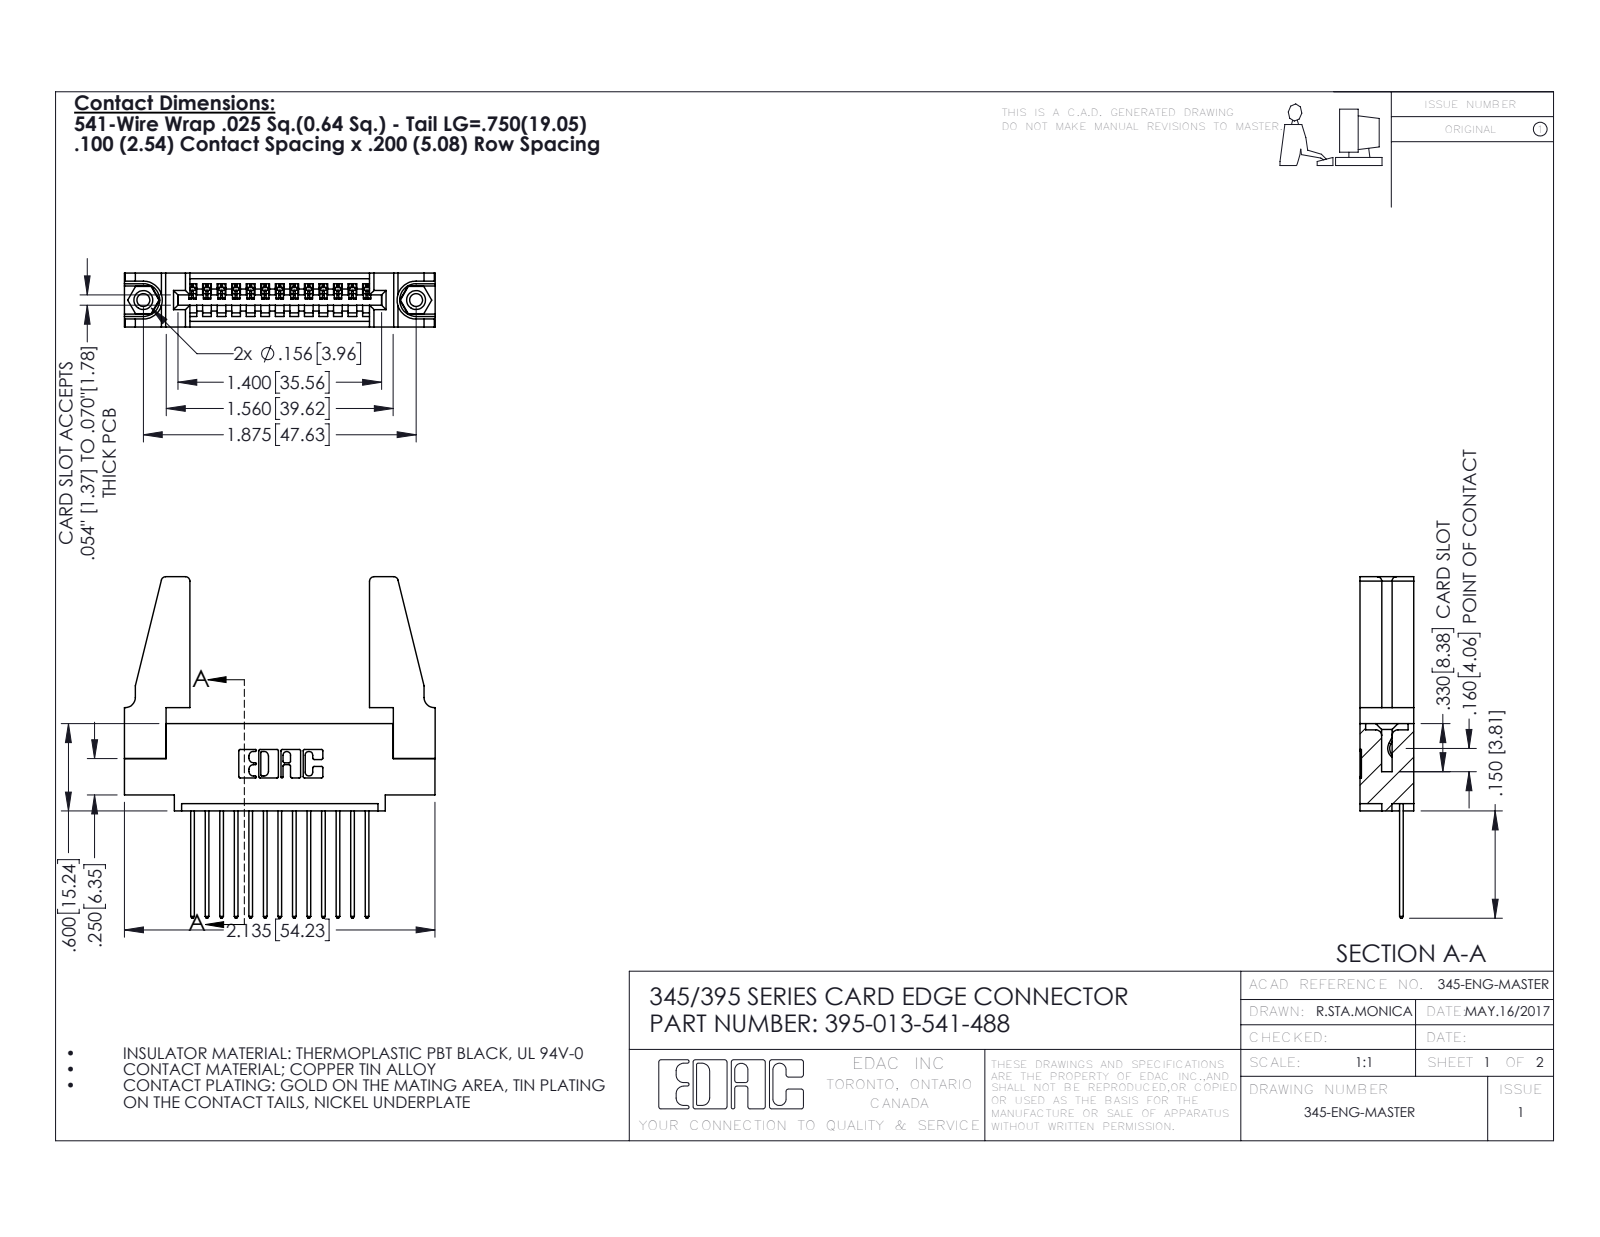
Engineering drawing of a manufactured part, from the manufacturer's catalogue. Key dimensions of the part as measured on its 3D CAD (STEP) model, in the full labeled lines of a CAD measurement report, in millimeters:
Part name (STEP PRODUCT): 345-250-001_345-250-001-102; 345-220-078_345-220-088; 345 Part_0.110 Offset - 0.156 Dia-TH; 395-013-541-488 (+1 more)
STEP written by: SolidWorks 2016 (CONFIG_CONTROL_DESIGN)
Units: millimetres
Bodies: 18 solids, 1008 faces (676 planar, 316 cylindrical, 16 other)
Overall size (bounding box): 59.6 × 54.3 × 9.4
Volume: 8 140 mm³ · Surface area: 9 561 mm²
Round holes (diameter × count): ⌀2.3 ×2, ⌀3.2 ×2, ⌀4 ×2, ⌀1.6 ×1
Round bosses / shafts (diameter × count): ⌀3.9 ×2
Partial cylindrical surfaces — rounded edges, fillets, slot ends (radius × count): R0.2 ×26, R0.3 ×26, R0.3 ×22, R0.8 ×8, R0.2 ×6, R0.8 ×6, R0.7 ×3, R0.8 ×2
Main face-to-face distances: 9.4, 1.8, 7.6, 2.5, 6.9, 0.6, 5.1, 5.7, 3.8, 3.8
Hole centre spacings: 6.9, 41.7, 47.6
